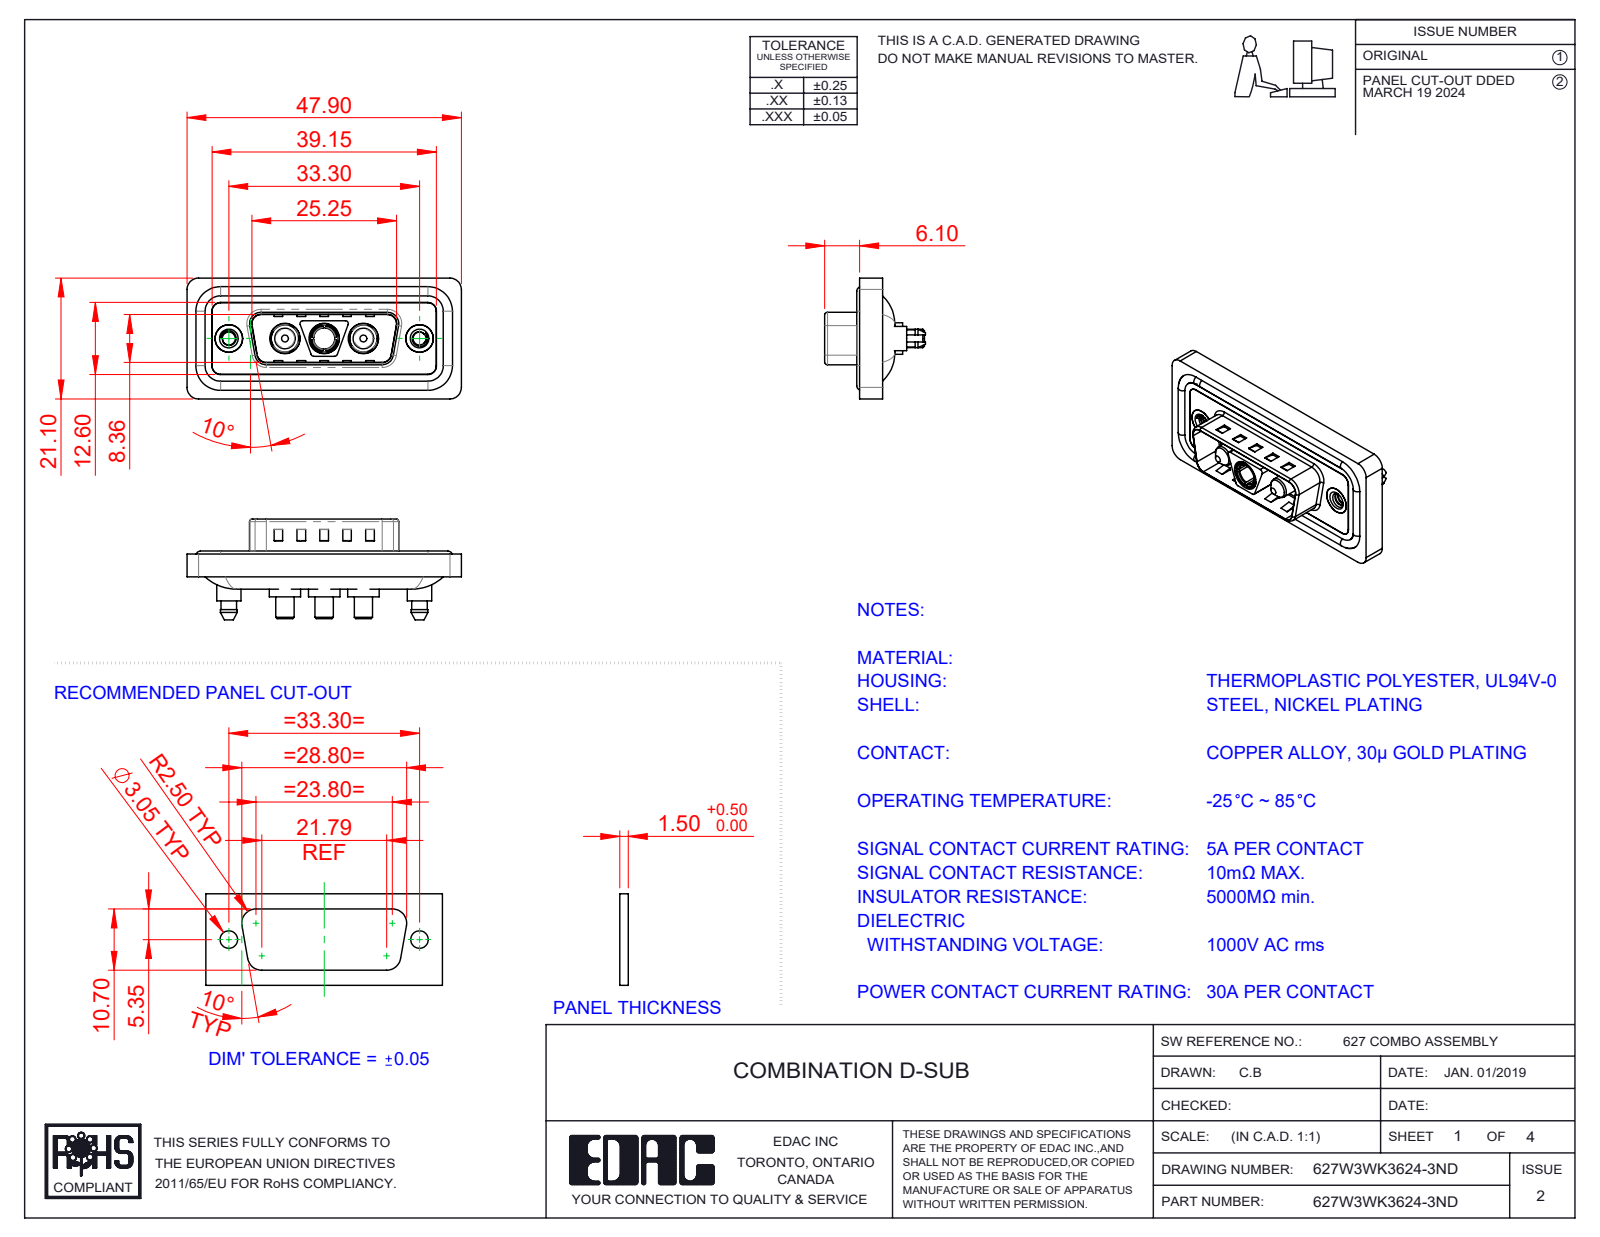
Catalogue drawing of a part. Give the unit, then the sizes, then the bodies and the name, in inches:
Units: inches
Overall size (bounding box): 1.886 × 0.831 × 0.693
Round holes (diameter × count): ⌀0.191 ×3, ⌀0.209 ×3, ⌀0.089 ×2, ⌀0.157 ×2, ⌀0.189 ×2, ⌀0.197 ×2, ⌀0.146 ×1
Round bosses / shafts (diameter × count): ⌀0.063 ×4, ⌀0.217 ×3, ⌀0.205 ×3, ⌀0.187 ×3, ⌀0.148 ×3, ⌀0.126 ×3, ⌀0.213 ×2, ⌀0.193 ×2
Partial cylindrical surfaces — rounded edges, fillets, slot ends (radius × count): R0.059 ×28, R0.079 ×20, R0.02 ×12, R0.063 ×10, R0.01 ×4, R0.024 ×4, R0.026 ×4, R0.035 ×4
Main face-to-face distances: 0.016, 0.043, 0.059, 0.02, 0.122, 0.063, 0.114, 0.157, 0.028, 0.032
Hole centre spacings: 0.27, 0.386, 0.656, 0.925, 0.539, 1.311
Volume: 0.357 in³ · Surface area: 14.69 in²
Bodies: 13 solids, 667 faces (247 planar, 290 cylindrical, 130 other)
Part name (STEP PRODUCT): Power Socket_30A S; Power Pin_30A S; 627Combo Shell Rear_15 Contacts; 627Combo Threaded Boardlock_5 (+5 more)
STEP written by: SolidWorks 2023 (CONFIG_CONTROL_DESIGN)
